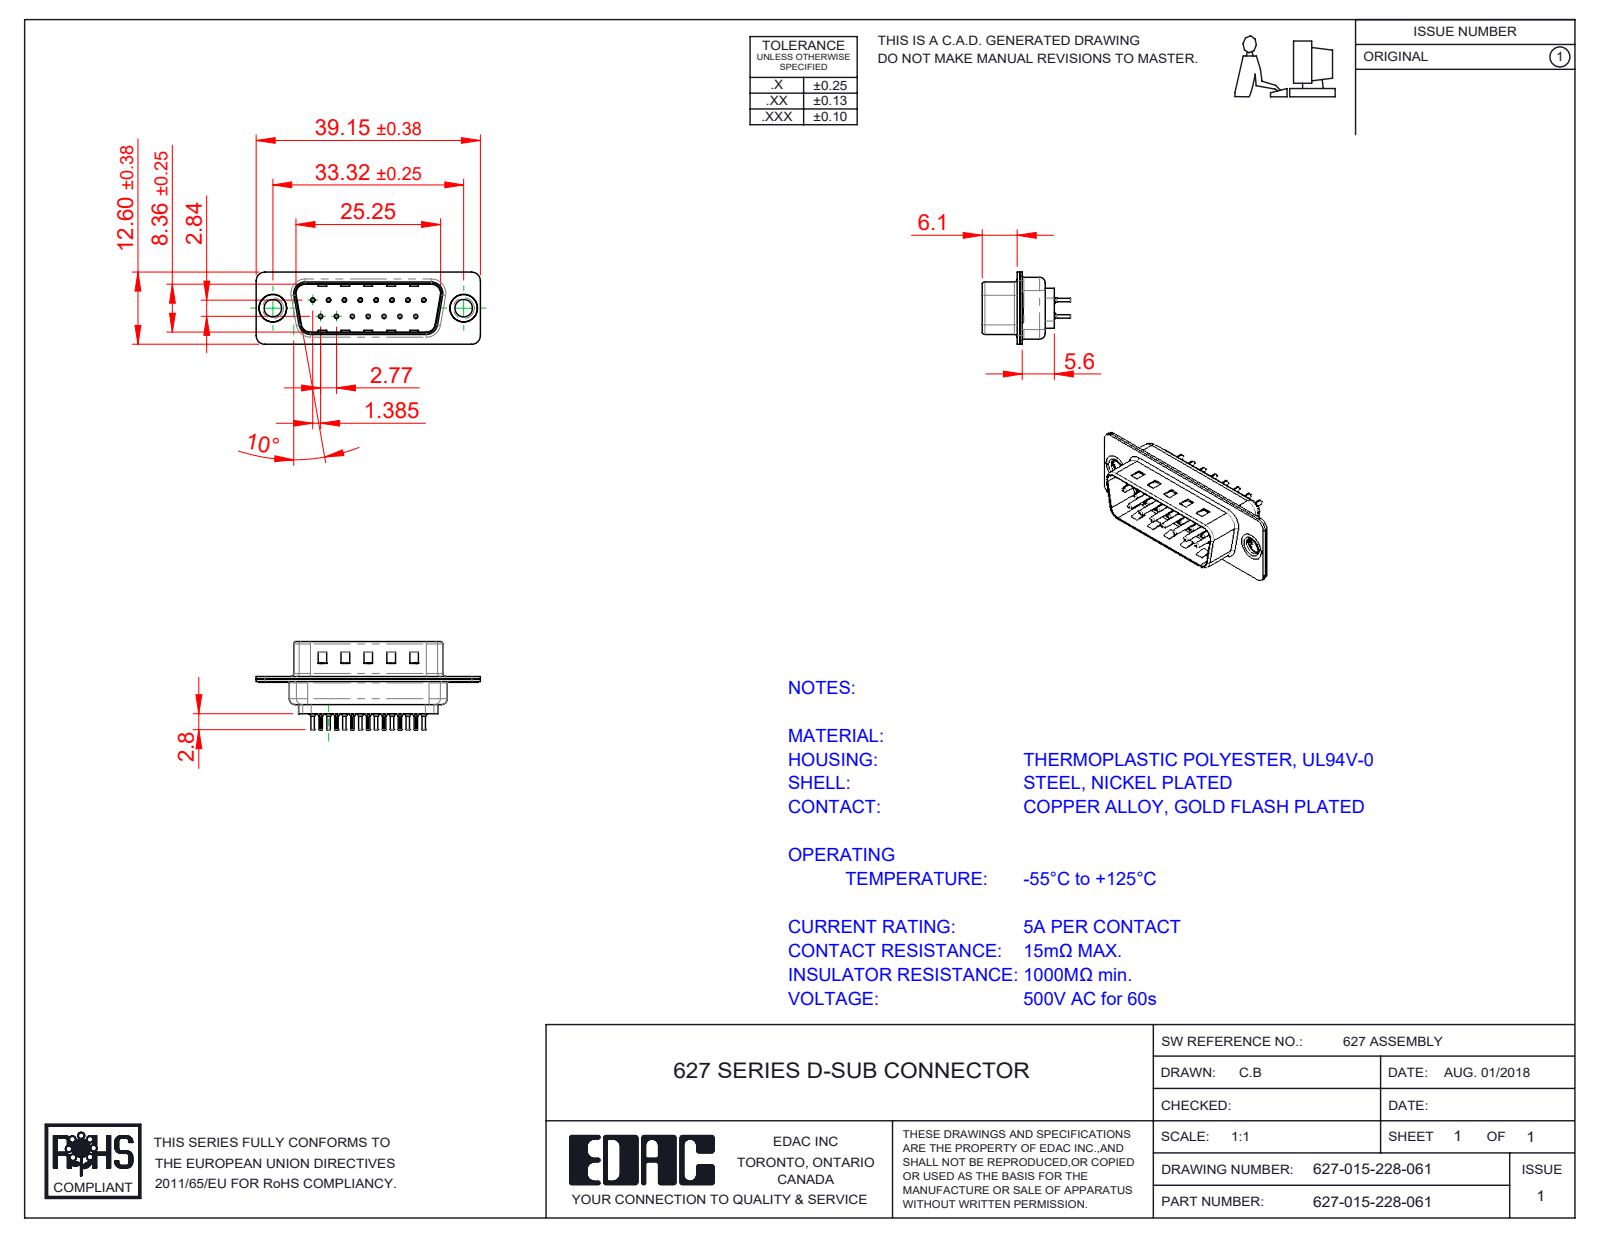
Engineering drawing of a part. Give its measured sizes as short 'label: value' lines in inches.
name: 627 Thru Hole Rivet; 627 Contact Row 2_28L; 627 Housing_15 FF; 627 Shell Front_15 Contacts (+3 more)
written by: SolidWorks 2020 (CONFIG_CONTROL_DESIGN)
unit: in
bodies: 21 solids, 1825 faces (505 planar, 707 cylindrical, 613 other)
size: 1.541 × 0.74 × 0.496
volume: 0.13 in³; area: 9.23 in²
holes: 15× ⌀0.008, 15× ⌀0.014, 15× ⌀0.043, 15× ⌀0.063, 2× ⌀0.12, 2× ⌀0.157, 2× ⌀0.189
bosses: 15× ⌀0.079, 15× ⌀0.059, 15× ⌀0.03, 15× ⌀0.024, 2× ⌀0.197, 2× ⌀0.193, 2× ⌀0.14
rounds: 30× R0.004, 16× R0.059, 12× R0.079, 8× R0.02, 8× R0.063, 4× R0.01, 4× R0.024, 4× R0.026
face distances: 0.016, 0.018, 0.035, 0.238, 0.032, 0.377, 0.331, 0.256, 0.059, 0.11
hole spacings: 0.124, 0.109, 0.218, 0.327, 0.436, 0.198, 0.198, 0.294
